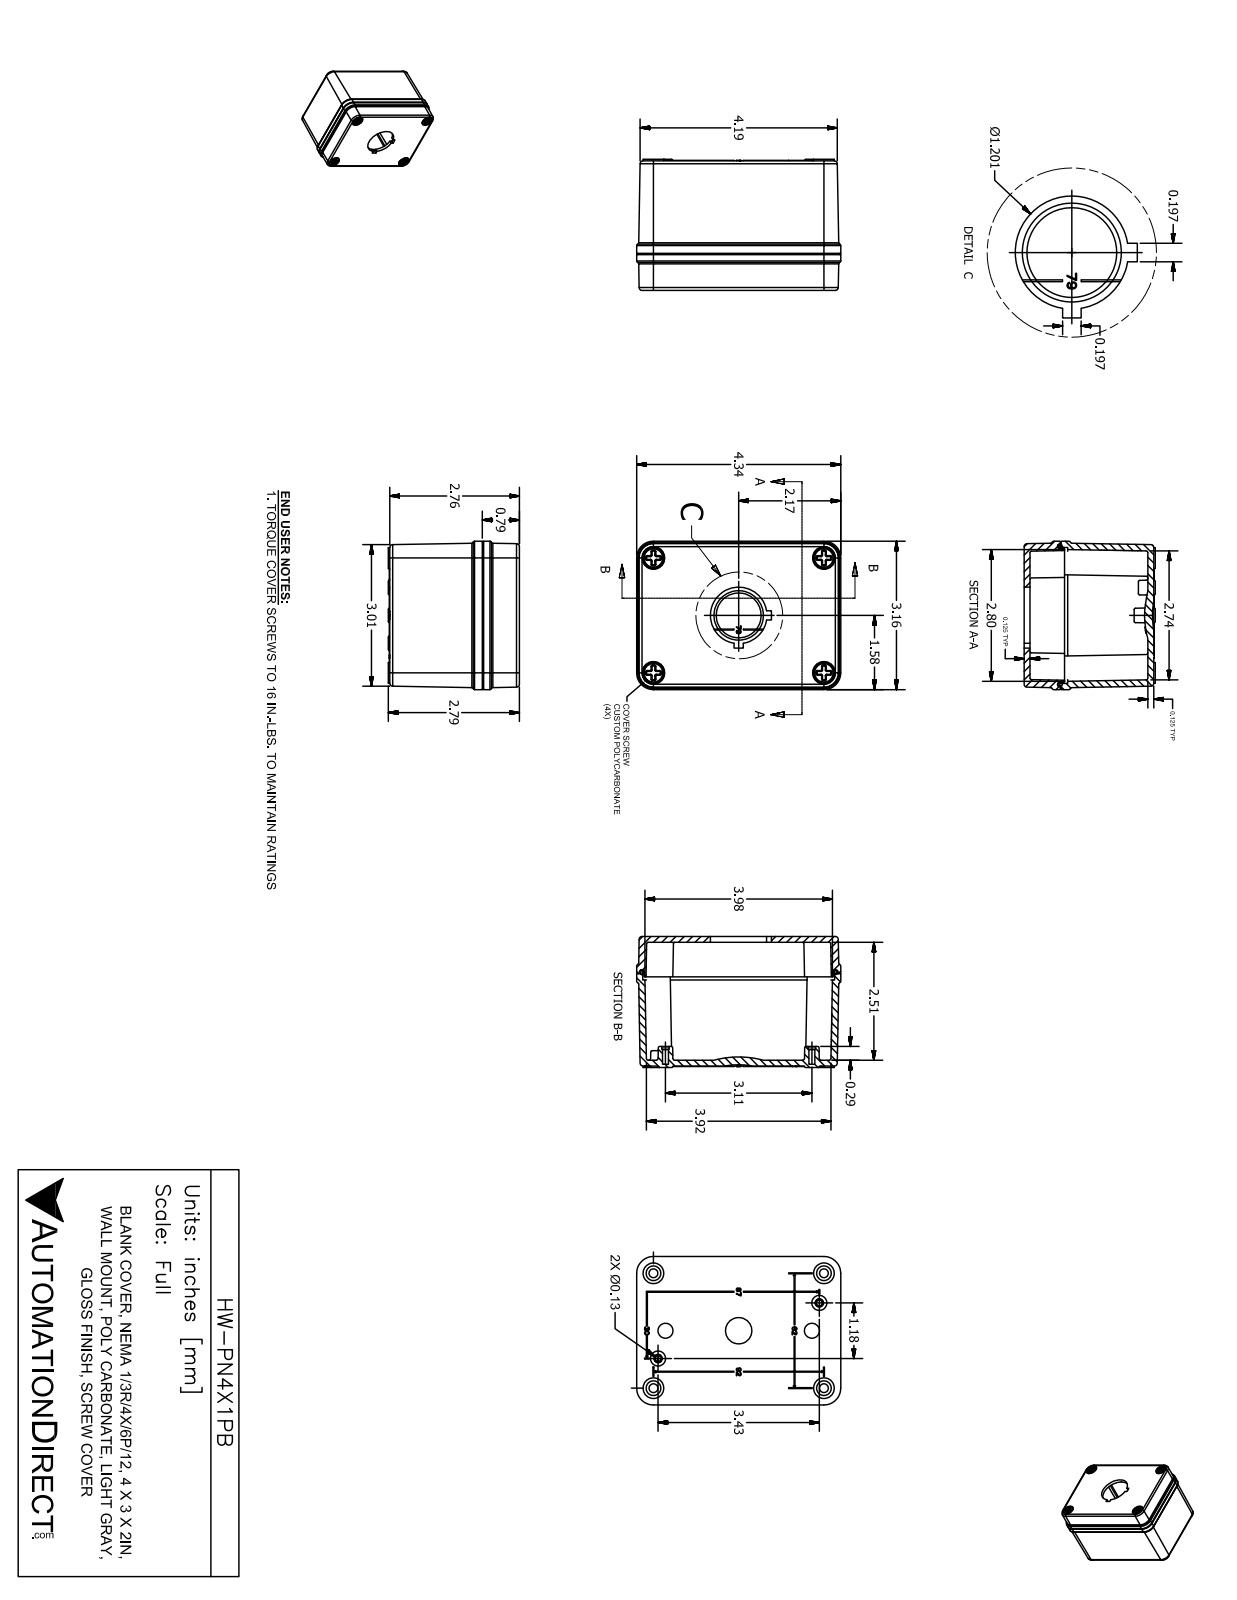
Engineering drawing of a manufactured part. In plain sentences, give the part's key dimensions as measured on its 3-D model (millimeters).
The part is named "HW-PN4X1PB". Its 3-D file was written by "SolidWorks 2017 (AUTOMOTIVE_DESIGN)". It is 7 solids with 1040 faces: 218 planar, 378 cylindrical and 444 other. Overall it measures 110.1 by 80.2 by 70.7 millimeters. Its volume is 163 000 cubic millimeters and its surface area 98 520 square millimeters. Round holes: 6 of diameter 2.5, 4 of diameter 4.7, 4 of diameter 10, 4 of diameter 11.7, 1 of diameter 30.5. Round bosses or shafts: 4 of diameter 12.7, 4 of diameter 11, 4 of diameter 7, 2 of diameter 2.5. Partial cylindrical surfaces (rounded edges, fillets, slot ends): 48 of radius 0.3, 48 of radius 0.5, 16 of radius 0.8, 12 of radius 0.4, 8 of radius 0.5, 8 of radius 0.5, 8 of radius 0.8, 8 of radius 1.6. The main face-to-face distances are 3.4, 70, 66.5, 66.8, 63.4, 3.2, 4.1, 49.9, 46.5, 16.9. The hole center spacings are 55.5, 14.5, 61.9, 62, 62, 62.1, 90.1, 91.8.
